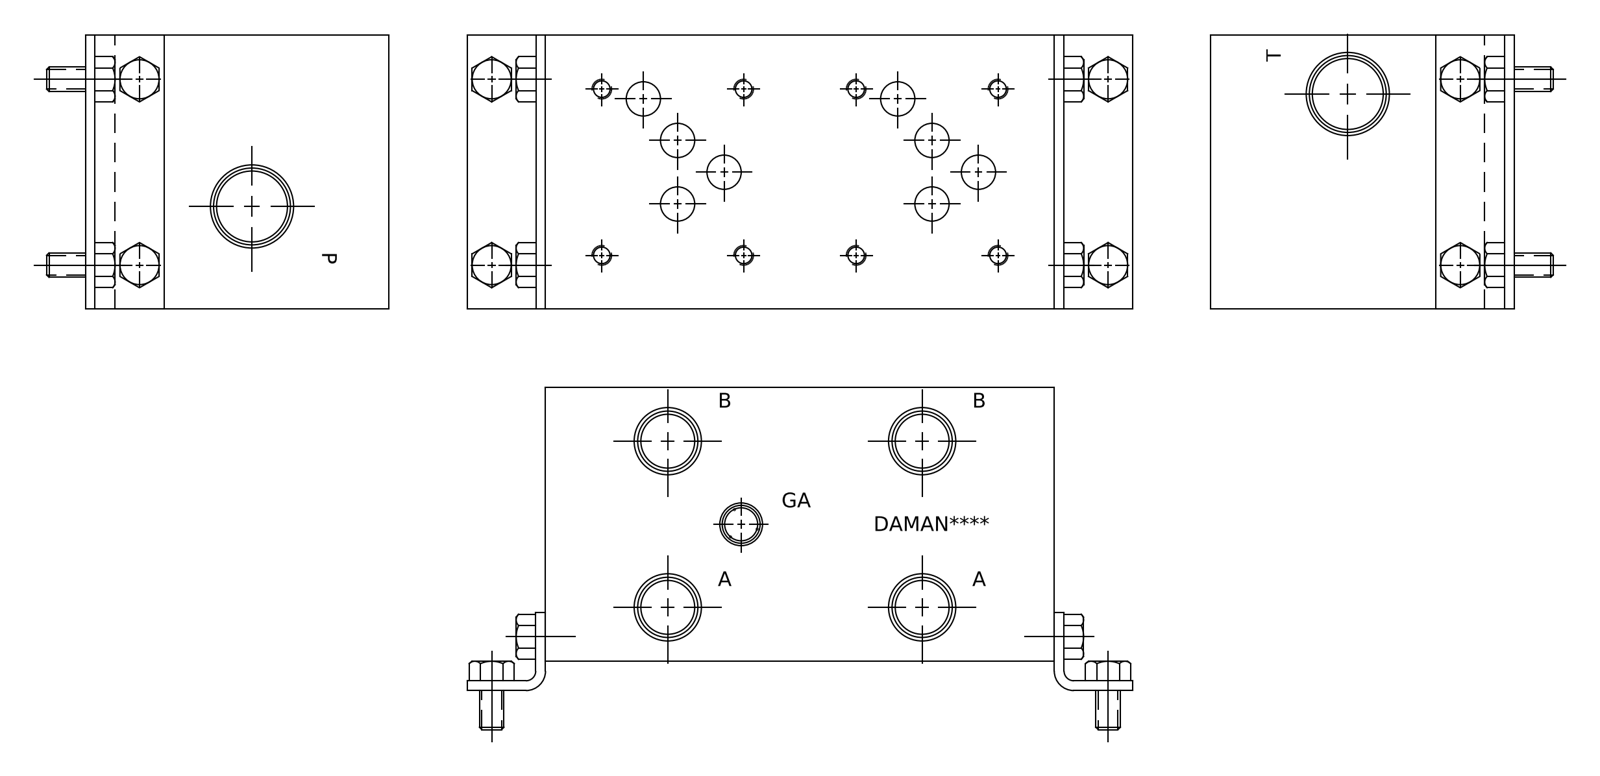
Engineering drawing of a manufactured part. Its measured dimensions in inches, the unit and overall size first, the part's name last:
Units: inches
Overall size (bounding box): 6.5 × 3.5 × 3.5
Round holes (diameter × count): ⌀0.201 ×8, ⌀0.25 ×8, ⌀0.438 ×8, ⌀0.688 ×4, ⌀0.85 ×4, ⌀0.257 ×2, ⌀0.312 ×2, ⌀0.906 ×2, ⌀1.06 ×2, ⌀0.422 ×1, ⌀0.546 ×1
Main face-to-face distances: 3.5, 6.5, 0.605, 2.895, 0.624, 5.876, 0.604, 3.498, 5.252, 2.75
Hole centre spacings: 3.25, 2.125, 3.883, 1.813, 2.793, 0.546, 0.719, 1.092
Volume: 76.04 in³ · Surface area: 137.1 in²
Bodies: 1 solid, 552 faces (322 planar, 46 cylindrical, 184 other)
Part name (STEP PRODUCT): Part_AD05S023P.C02246R4_3D
STEP written by: Autodesk Inventor 2020 (AUTOMOTIVE_DESIGN)
